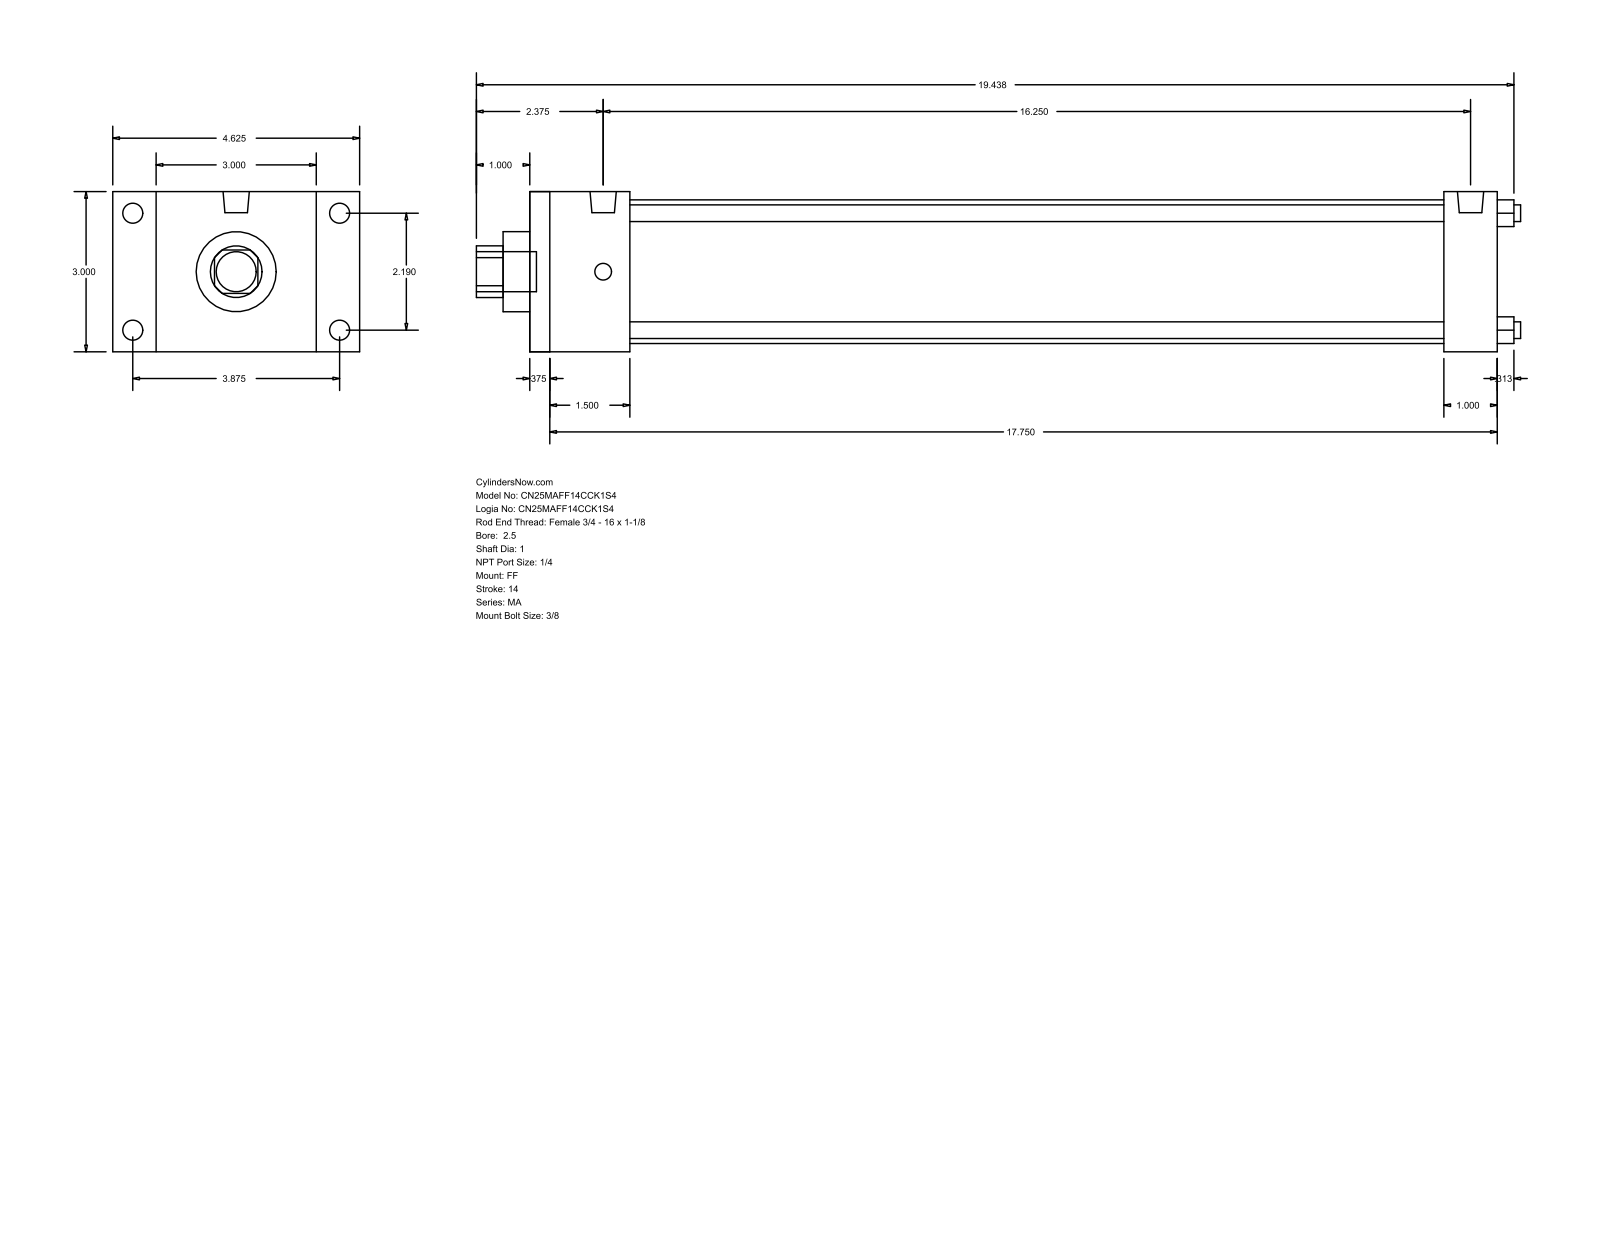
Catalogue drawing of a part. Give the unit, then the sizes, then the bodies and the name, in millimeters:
Units: millimetres
Overall size (bounding box): 496.89 × 117.47 × 76.2
Round holes (diameter × count): ⌀7.94 ×4, ⌀25.4 ×1, ⌀38.1 ×1, ⌀68.33 ×1
Round bosses / shafts (diameter × count): ⌀9.53 ×4, ⌀7.94 ×4, ⌀12.49 ×2, ⌀19.05 ×1
Partial cylindrical surfaces — rounded edges, fillets, slot ends (radius × count): R12.29 ×1
Main face-to-face distances: 76.2, 460.37, 450.85, 9.52, 25.39, 47.63, 434.98, 38.11, 425.46, 387.35
Hole centre spacings: 39.33, 55.62, 78.66
Bodies: 0 solids, 92 faces (64 planar, 28 cylindrical, 0 other)
Part name (STEP PRODUCT): MA_FF__0250_1
STEP written by: GSSL Pune (CONFIG_CONTROL_DESIGN)
